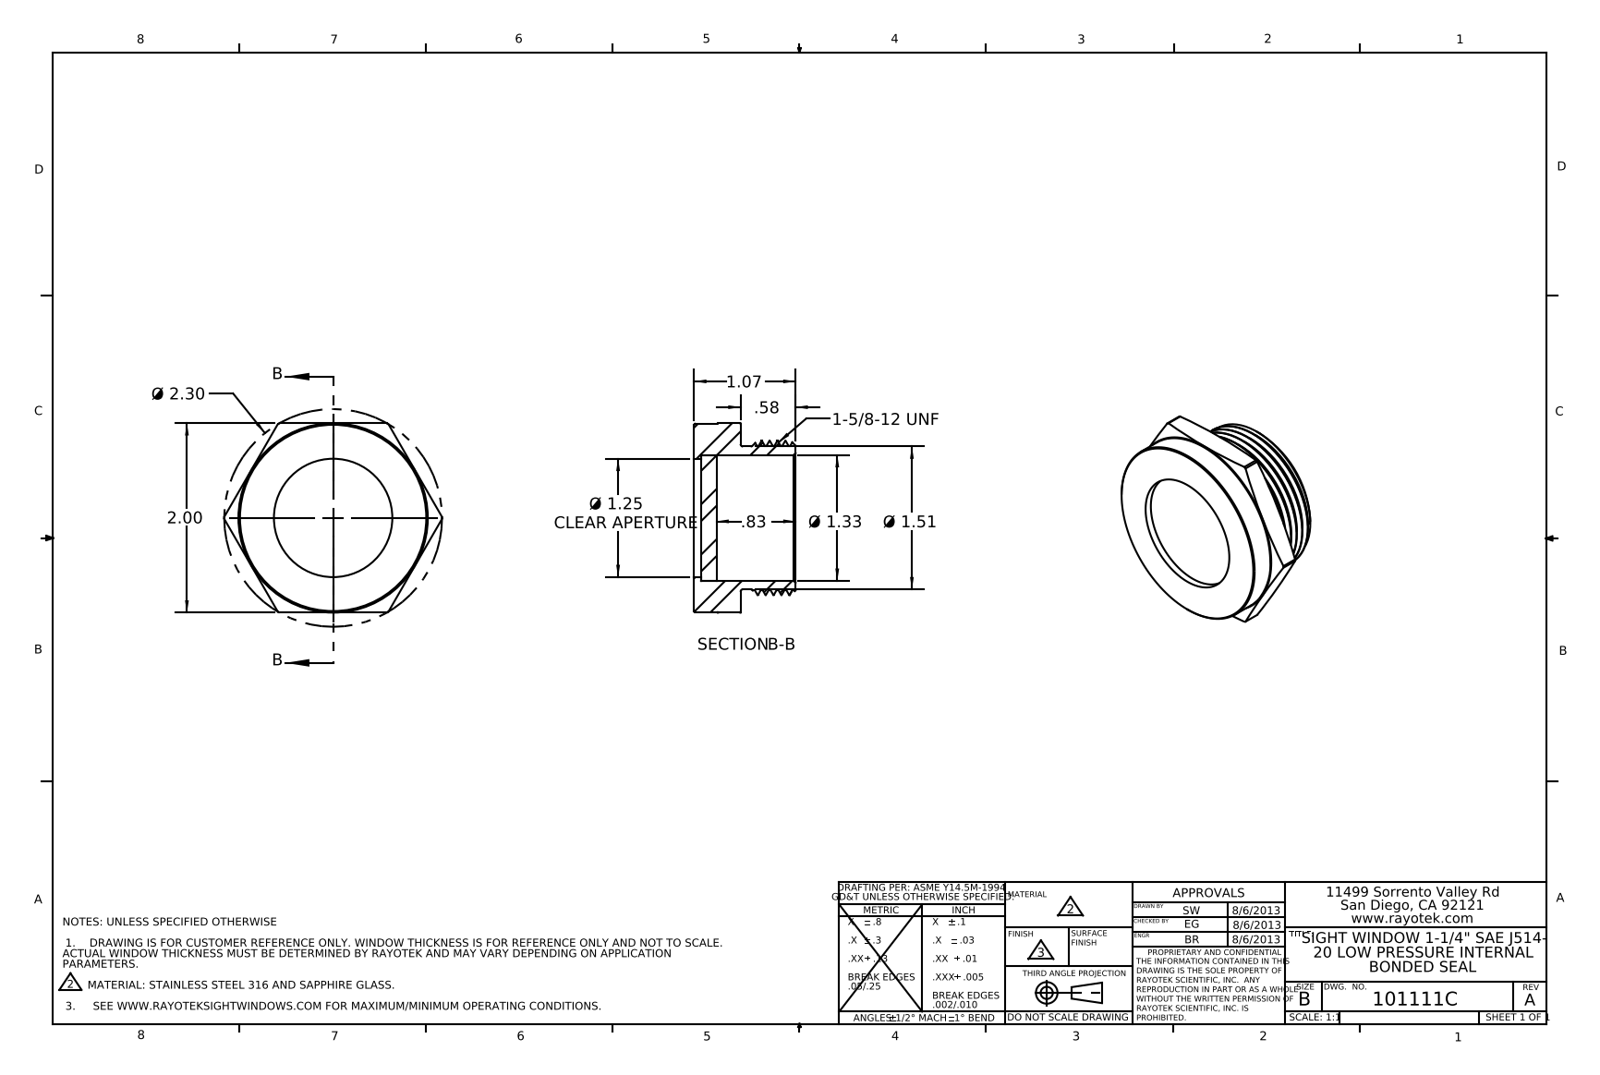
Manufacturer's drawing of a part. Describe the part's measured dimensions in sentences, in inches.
The part is named "403111". Its 3-D file was written by "SolidWorks 2012 (AUTOMOTIVE_DESIGN)". It is 2 solids with 61 faces: 12 planar, 26 cylindrical and 23 other. Overall it measures 2.297 by 2 by 1.07 inches. Its volume is 1.443 cubic inches and its surface area 19.59 square inches. Round holes: 1 of diameter 1.249, 1 of diameter 1.327. Round bosses or shafts: 1 of diameter 1.985, 1 of diameter 1.625, 1 of diameter 1.507. Partial cylindrical surfaces (rounded edges, fillets, slot ends): 1 of radius 1.149. The main face-to-face distances are 0.078, 0.157, 0.236, 0.254, 0.412, 0.49, 2, 0.58, 0.834, 0.992.
